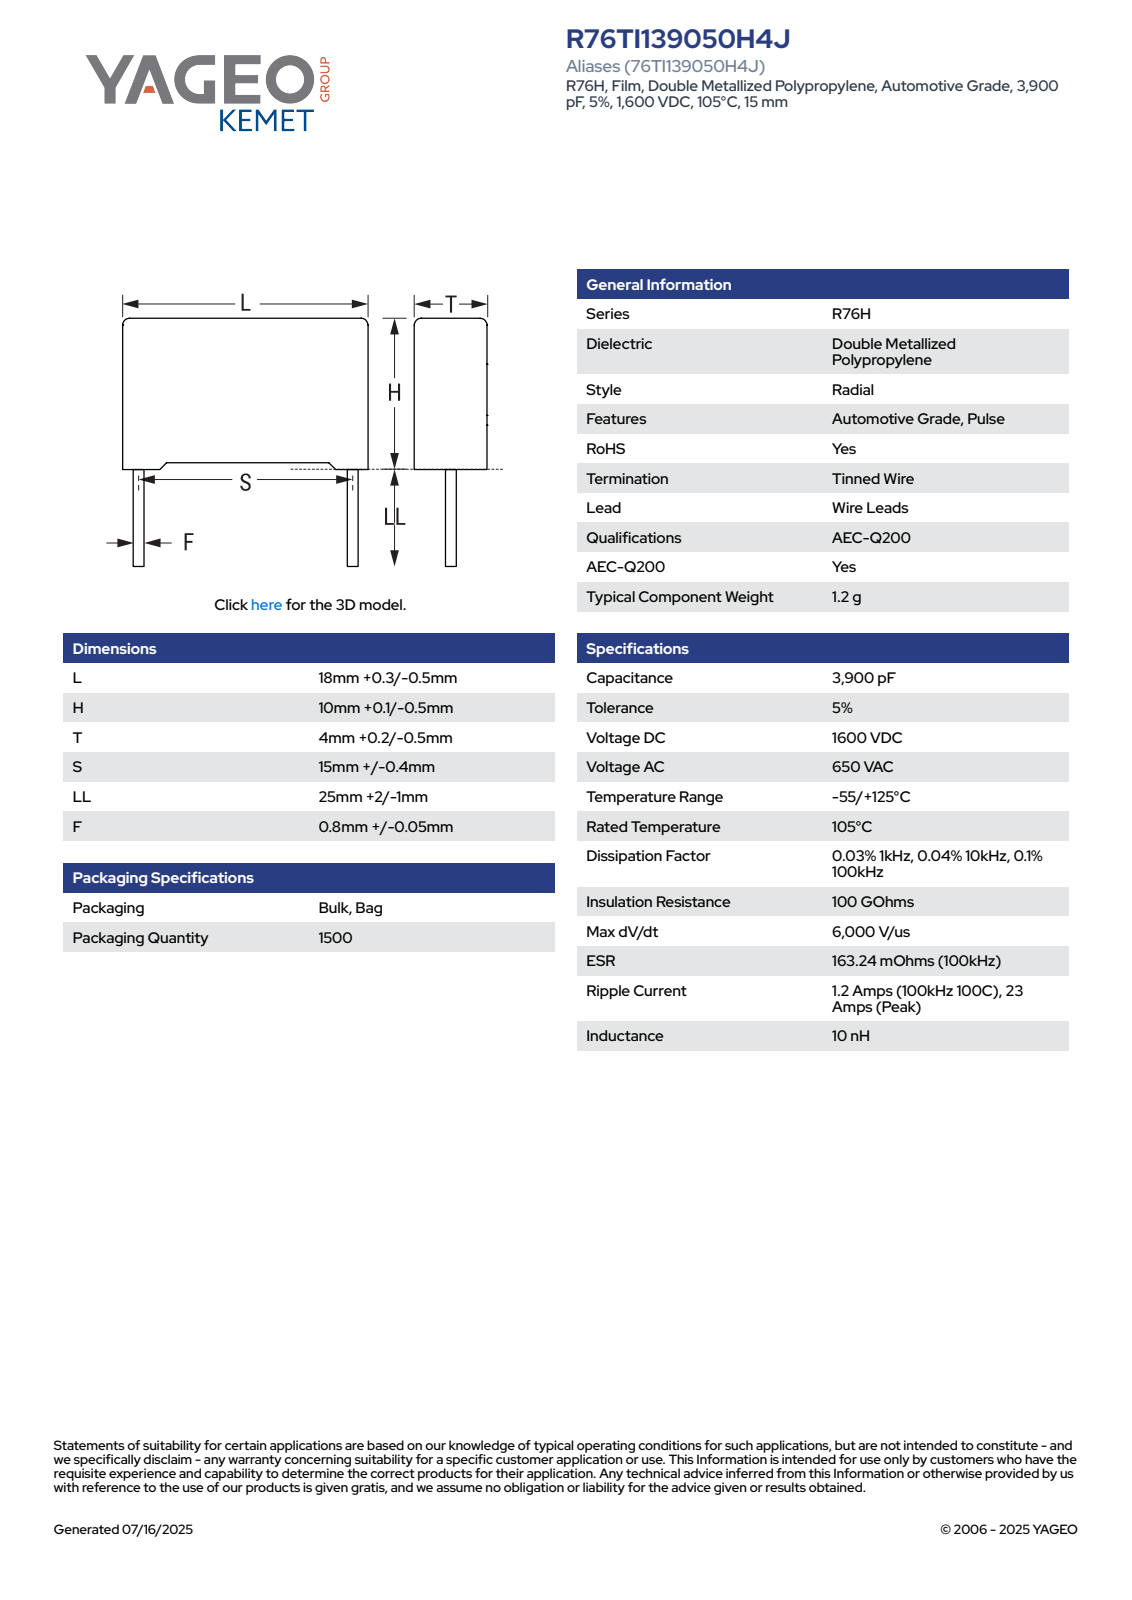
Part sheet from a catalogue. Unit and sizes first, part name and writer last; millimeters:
Units: millimetres
Overall size (bounding box): 37.1 × 18.3 × 4.21
Round bosses / shafts (diameter × count): ⌀0.85 ×2
Partial cylindrical surfaces — rounded edges, fillets, slot ends (radius × count): R0.5 ×4
Main face-to-face distances: 4.2, 9.35, 18.3, 0.61, 3.59, 0.4, 9.75, 0.75, 0.35, 10.1
Volume: 762 mm³ · Surface area: 786 mm²
Bodies: 4 solids, 85 faces (77 planar, 8 cylindrical, 0 other)
Part name (STEP PRODUCT): CFR_RB2R76_18X10X4_L18.3H10.1T4.2S15LL27F0.85
STEP written by: SolidWorks 2014 (AUTOMOTIVE_DESIGN)
